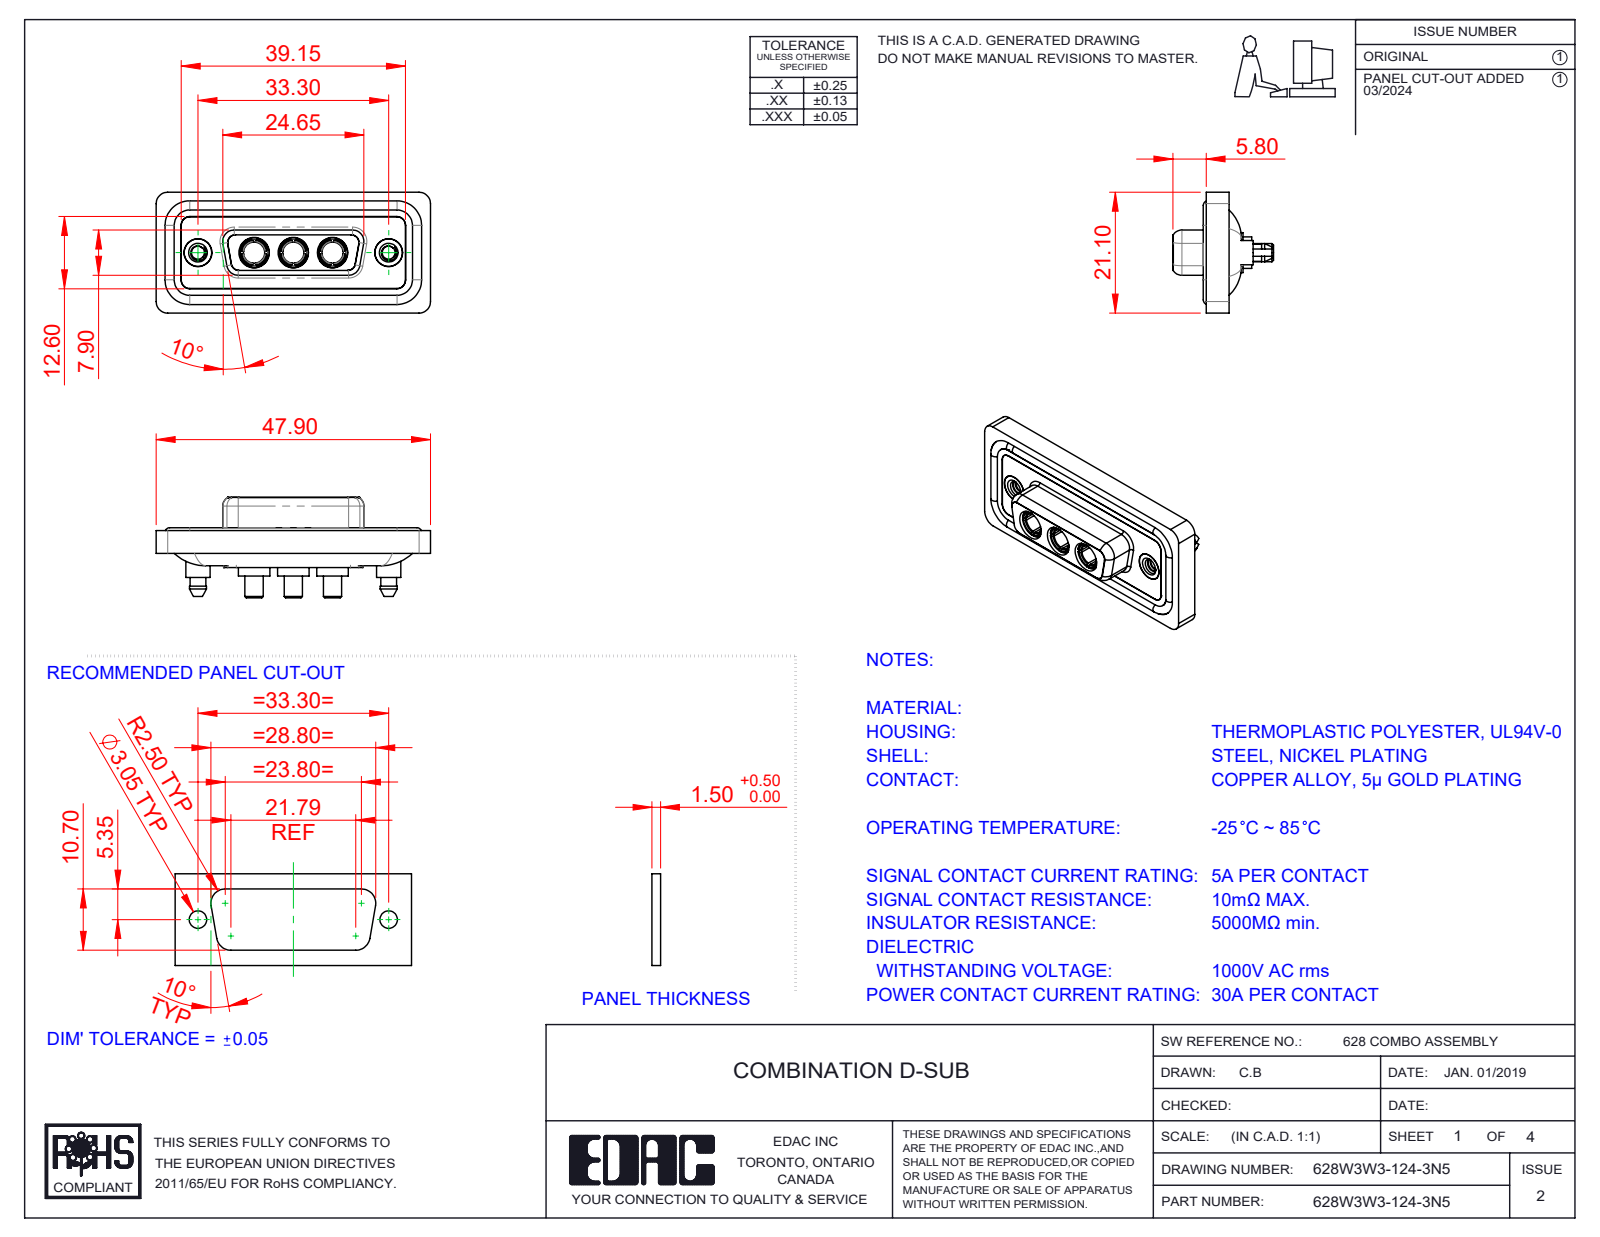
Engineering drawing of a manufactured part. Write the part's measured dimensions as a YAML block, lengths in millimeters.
part_name: "628Combo Housing_3W3; Power Socket_30A S; 628Combo Shell Rear_15 Contacts; 628Combo Shell Front_15 Contacts (+3 more)"
step_written_by: "SolidWorks 2023 (CONFIG_CONTROL_DESIGN)"
units: millimeters
bodies: {solids: 13, faces: 658, planar: 208, cylindrical: 289, other: 161}
overall_size: [47.9, 21.1, 17.55]
volume: 6181
surface_area: 10085
round_holes:
  - {diameter: 4.85, count: 5}
  - {diameter: 3.7, count: 3}
  - {diameter: 5.3, count: 3}
  - {diameter: 2.26, count: 2}
  - {diameter: 4, count: 2}
  - {diameter: 4.05, count: 2}
  - {diameter: 5, count: 2}
round_bosses_or_shafts:
  - {diameter: 1.6, count: 4}
  - {diameter: 5.5, count: 3}
  - {diameter: 5.2, count: 3}
  - {diameter: 4.96, count: 3}
  - {diameter: 4.75, count: 3}
  - {diameter: 3.75, count: 3}
  - {diameter: 3.2, count: 3}
  - {diameter: 5.4, count: 2}
partial_cylinders:
  - {radius: 1.5, count: 24}
  - {radius: 2, count: 20}
  - {radius: 1.35, count: 12}
  - {radius: 1.6, count: 10}
  - {radius: 0.25, count: 4}
  - {radius: 0.5, count: 4}
  - {radius: 0.6, count: 4}
  - {radius: 0.65, count: 4}
face_to_face_distances: [0.4, 1.8, 1.6, 0.5, 7.45, 1.1, 2.9, 5.65, 7.05, 6.6]
hole_center_spacings: [6.85, 9.8, 16.65, 23.5, 13.7, 33.3]
